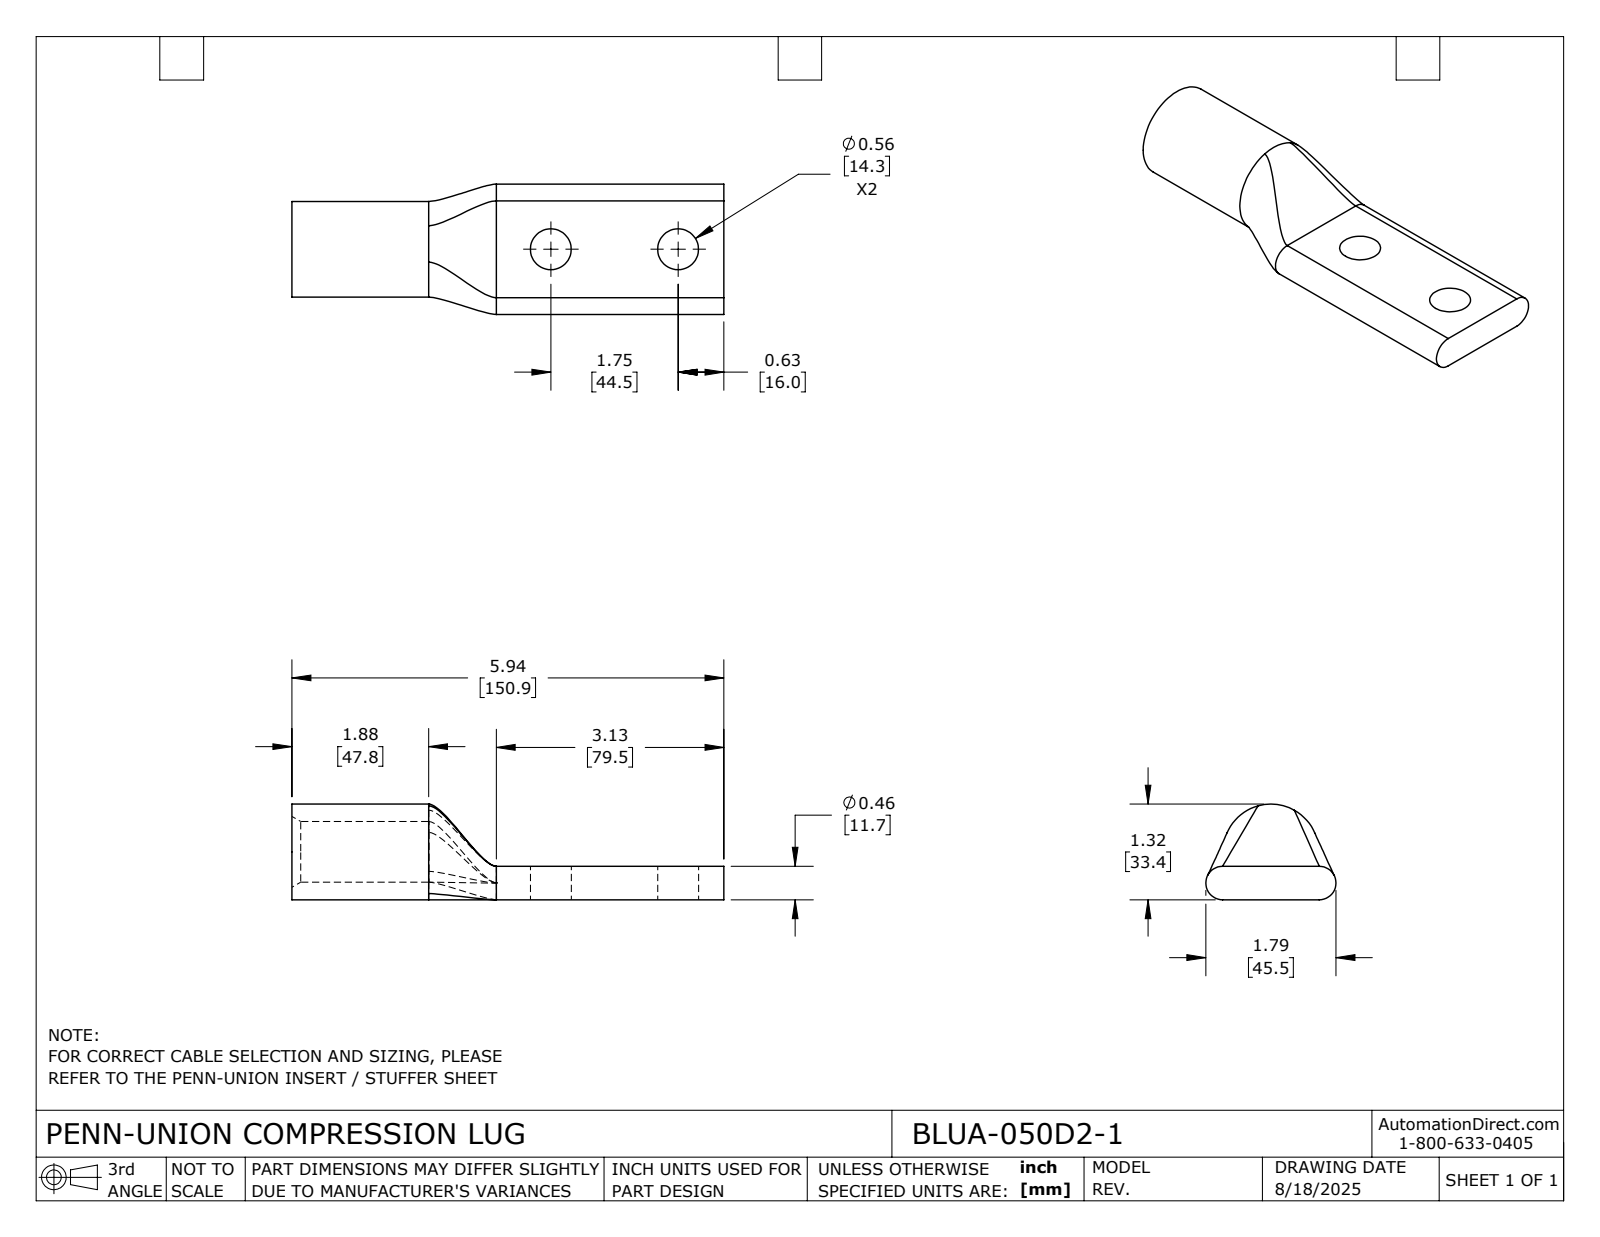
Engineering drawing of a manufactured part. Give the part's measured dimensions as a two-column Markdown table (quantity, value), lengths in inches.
| quantity | value |
| --- | --- |
| part name | BLUA-050D2-1 |
| STEP written by | SolidWorks 2024 (CONFIG_CONTROL_DESIGN) |
| units | inches |
| bodies | 1 solid, 26 faces (5 planar, 11 cylindrical, 10 other) |
| overall size | 5.94 × 1.79 × 1.315 |
| volume | 4.456 in³ |
| surface area | 34.62 in² |
| round holes (diameter × count) | 0.562 × 2, 0.834 × 1 |
| round bosses / shafts (diameter × count) | 1.315 × 1 |
| partial cylindrical surfaces (radius × count) | 0.23 × 2 |
| main face-to-face distances | 0.46, 5.94, 2.81, 3.13 |
| hole center spacings | 1.75 |
